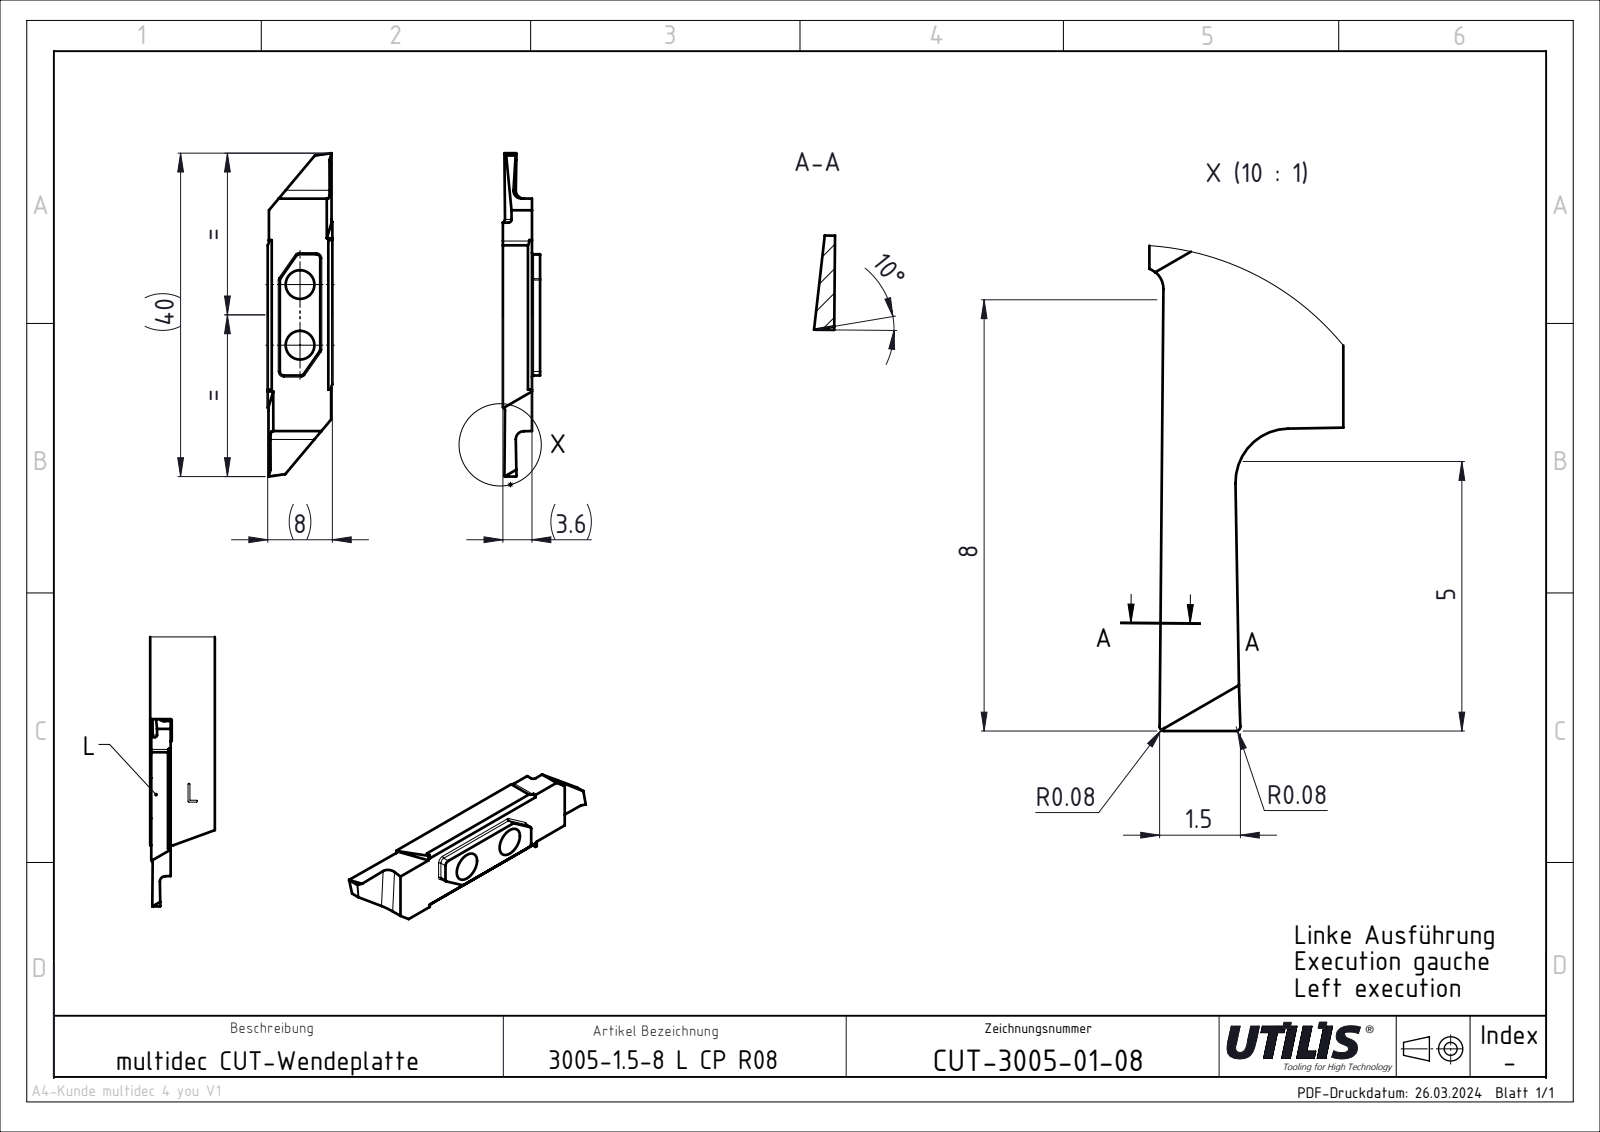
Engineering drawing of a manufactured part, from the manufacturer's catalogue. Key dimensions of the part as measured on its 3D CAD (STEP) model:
Part name (STEP PRODUCT): CUT-3005 CP; ASME Y14.5
STEP written by: SolidWorks 2023 SP4 || FormatWorks Professional (AP242_MANAGED_MODEL_BASED_3D_ENGINEERING_MIM_LF)
Units: millimetres
Bodies: 1 solid, 36 faces (22 planar, 14 cylindrical, 0 other)
Overall size (bounding box): 40 × 8 × 3.6
Volume: 800 mm³ · Surface area: 853 mm²
Round holes (diameter × count): ⌀3.55 ×2
Partial cylindrical surfaces — rounded edges, fillets, slot ends (radius × count): R1 ×4, R0.4 ×2
Main face-to-face distances: 3.6, 8, 7.85, 22.54, 7.7, 40, 10.75, 29.25, 18.5
Hole centre spacings: 7.49
